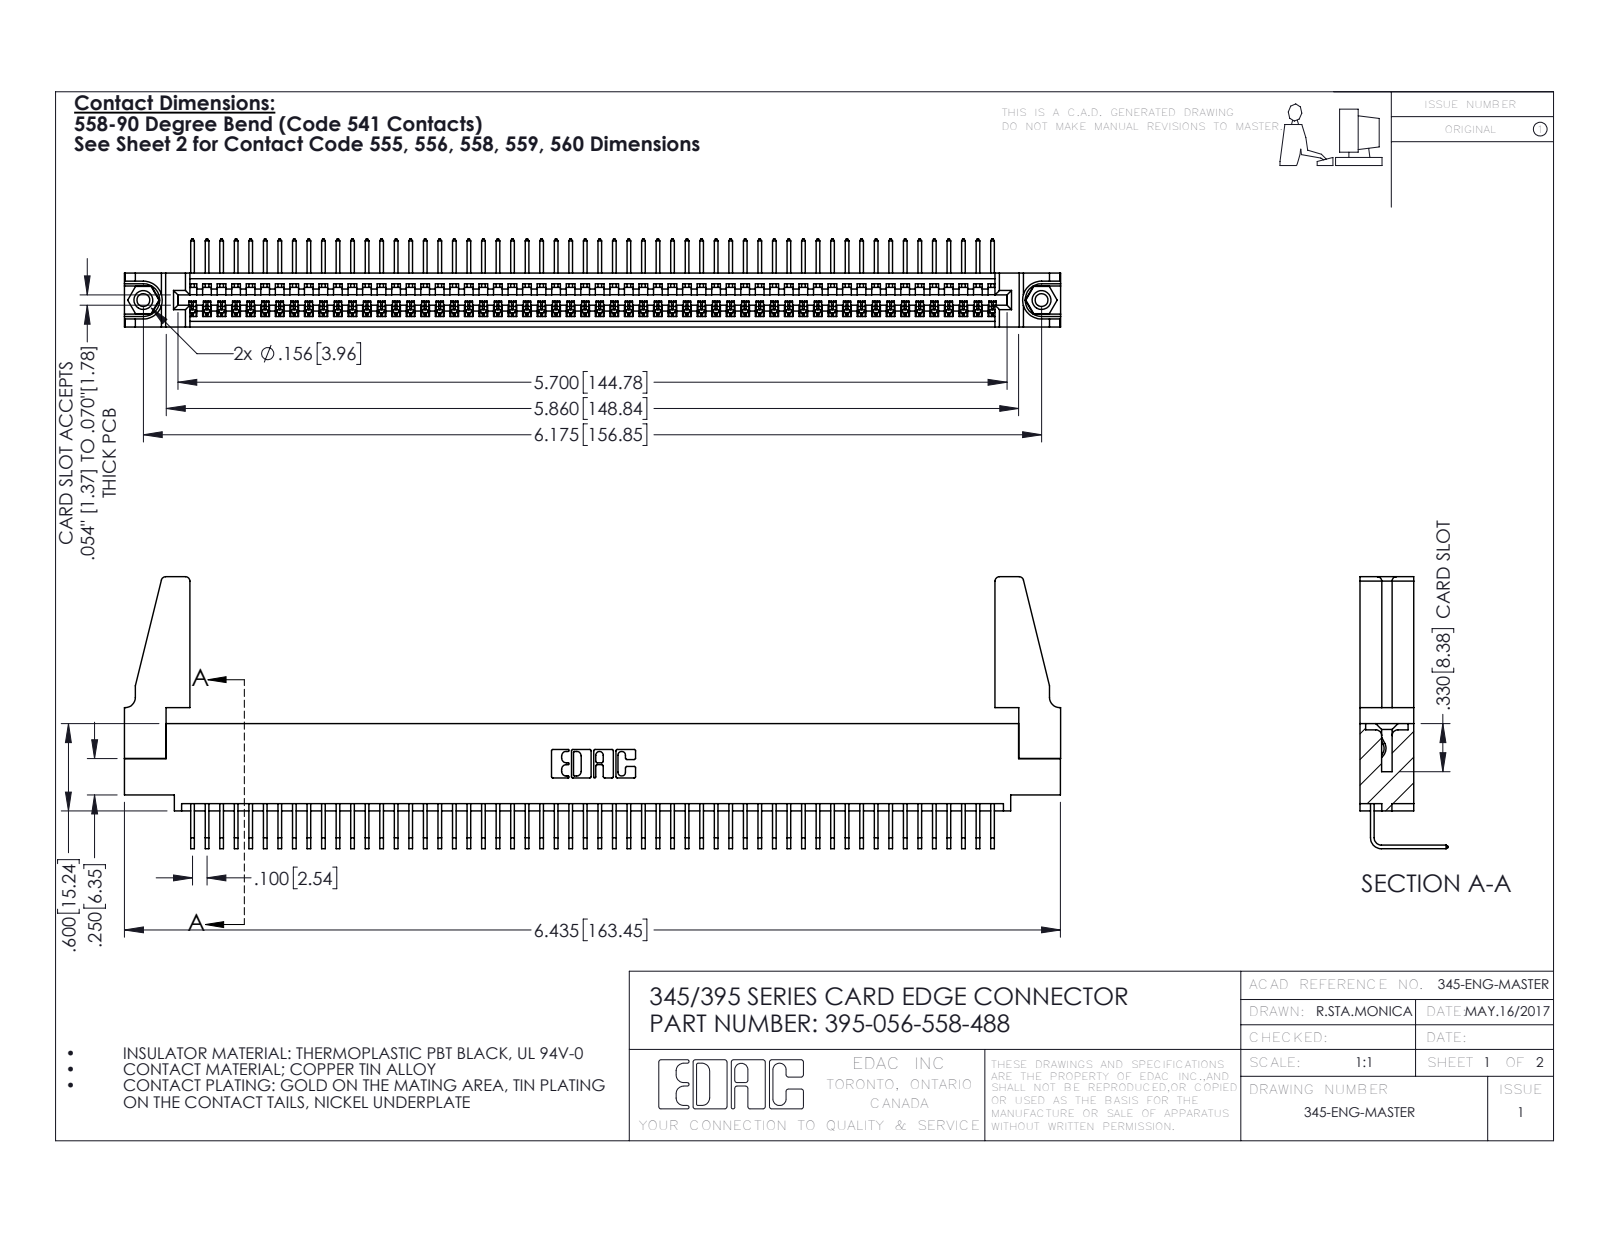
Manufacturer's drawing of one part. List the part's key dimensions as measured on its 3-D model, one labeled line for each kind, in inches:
Part name (STEP PRODUCT): 345-292-001_558 Tail - 2; 395-056-558-488; 345 Part_0.110 Offset - 0.156 Dia-TH; 345-220-078_345-220-088 (+1 more)
STEP written by: SolidWorks 2016 (CONFIG_CONTROL_DESIGN)
Units: inches
Bodies: 61 solids, 3614 faces (2508 planar, 1090 cylindrical, 16 other)
Overall size (bounding box): 6.436 × 1.869 × 0.605
Volume: 1.16 in³ · Surface area: 39.42 in²
Round holes (diameter × count): ⌀0.089 ×2, ⌀0.125 ×2, ⌀0.156 ×2, ⌀0.064 ×1
Round bosses / shafts (diameter × count): ⌀0.155 ×2
Partial cylindrical surfaces — rounded edges, fillets, slot ends (radius × count): R0.006 ×112, R0.01 ×22, R0.03 ×8, R0.007 ×6, R0.031 ×6, R0.026 ×3, R0.031 ×2, R0.04 ×2
Main face-to-face distances: 0.072, 0.298, 0.37, 0.2, 0.098, 0.272, 0.025, 0.225, 0.149, 0.072
Hole centre spacings: 0.27, 5.939, 6.175
